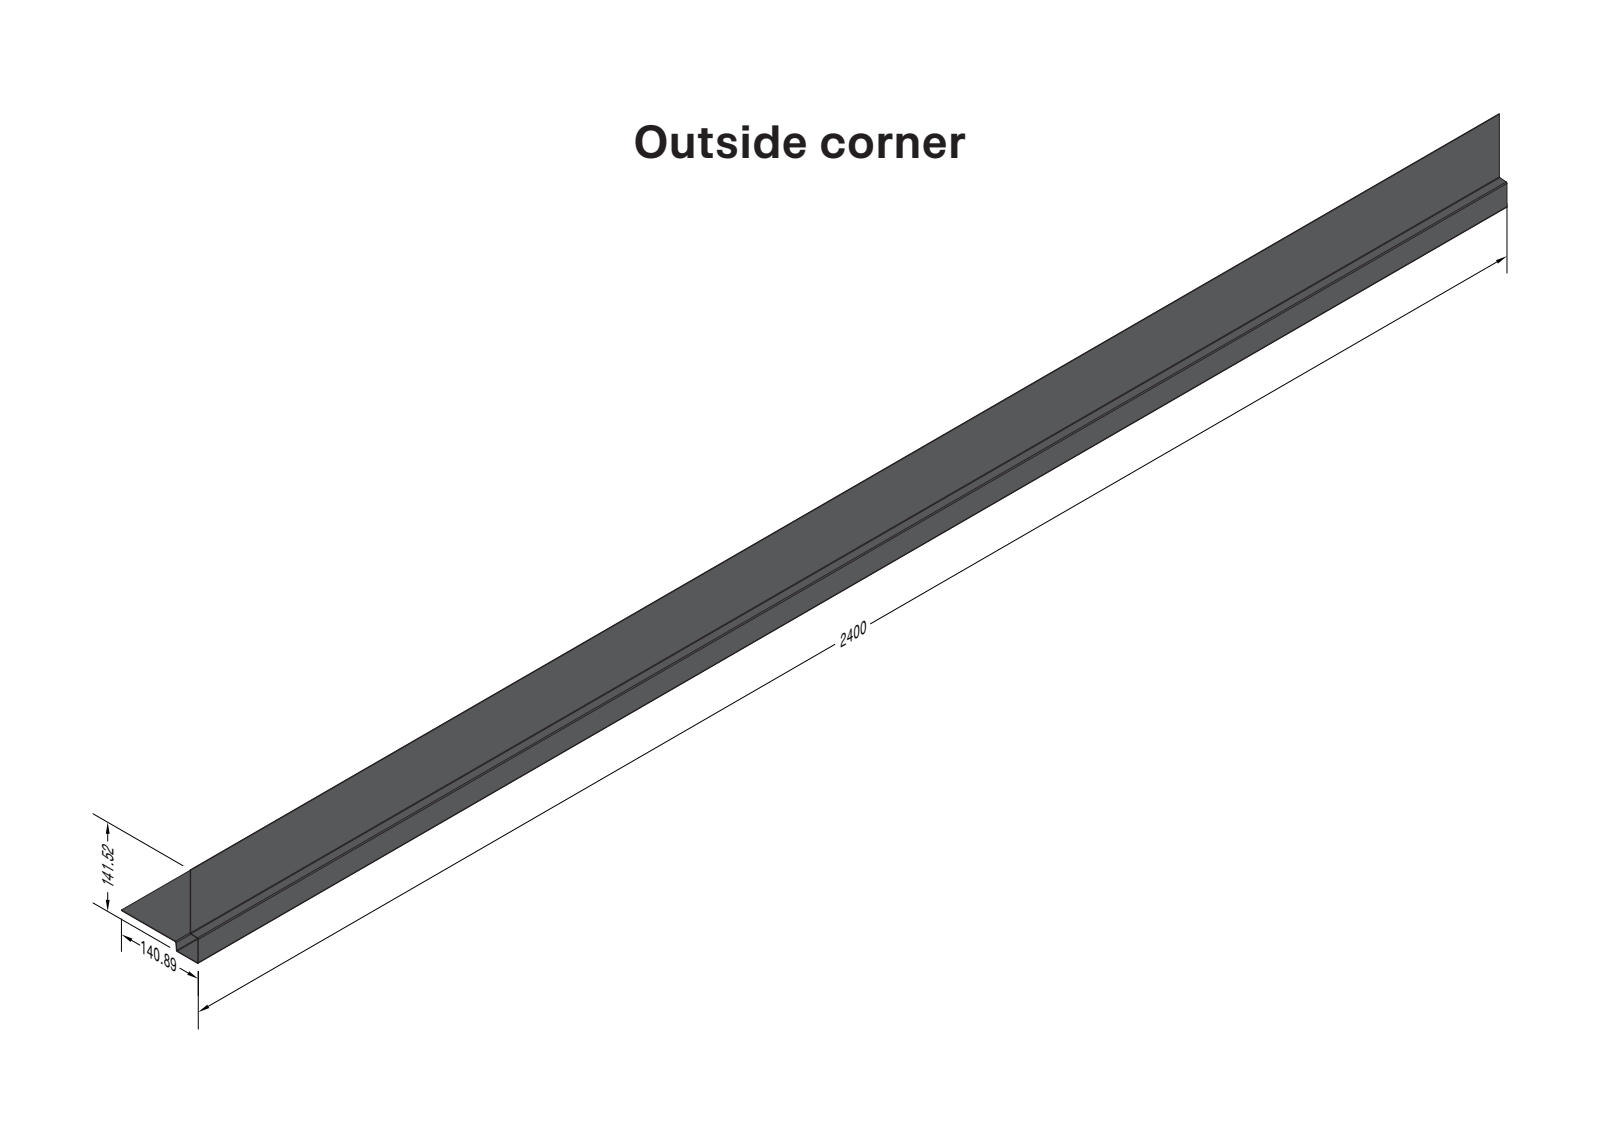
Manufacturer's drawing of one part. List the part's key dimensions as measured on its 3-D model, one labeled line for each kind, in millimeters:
Part name (STEP PRODUCT): Outside corner
STEP written by: Autodesk Inventor 2025 (AUTOMOTIVE_DESIGN)
Units: millimetres
Bodies: 1 solid, 46 faces (36 planar, 10 cylindrical, 0 other)
Overall size (bounding box): 2400 × 141.52 × 140.89
Volume: 585 560 mm³ · Surface area: 1 468 000 mm²
Partial cylindrical surfaces — rounded edges, fillets, slot ends (radius × count): R0.8 ×5, R1.6 ×5
Main face-to-face distances: 0.8, 13.95, 14.75, 13.15, 141.52, 140.72, 127.57, 126.77, 140.89, 140.09
